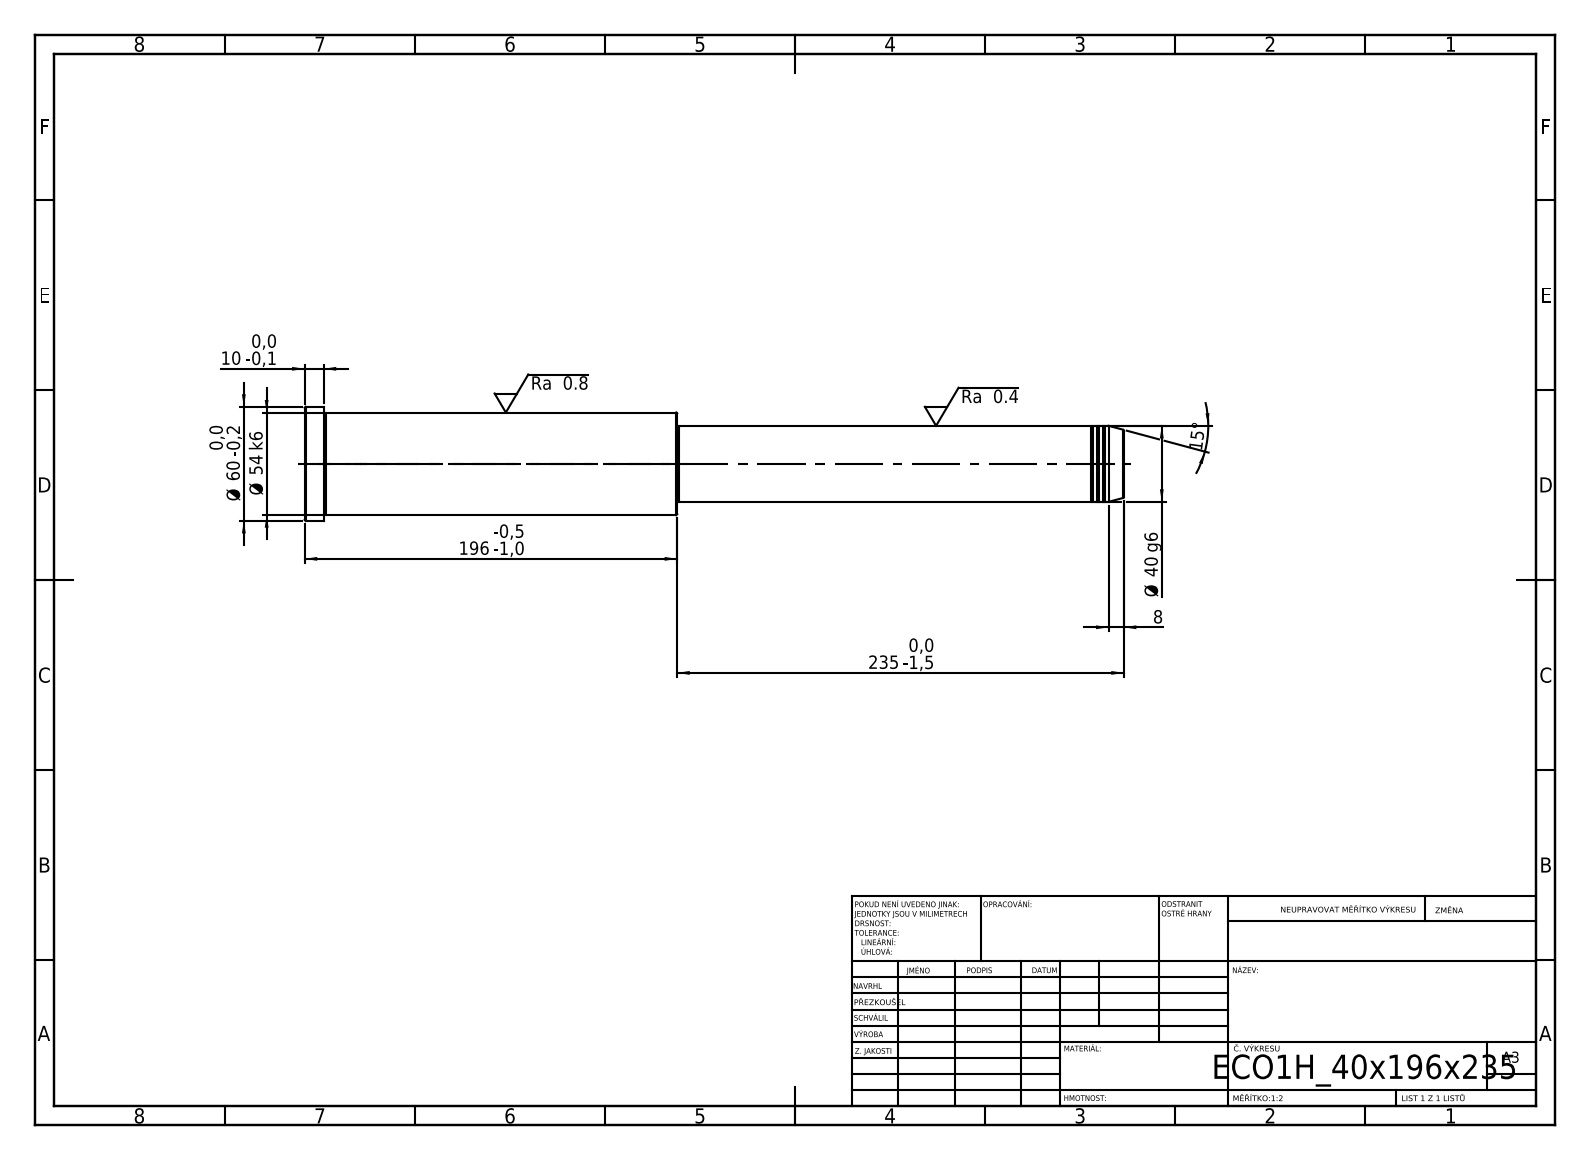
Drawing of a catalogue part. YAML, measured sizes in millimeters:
step_written_by: "SolidWorks 2019 (CONFIG_CONTROL_DESIGN)"
units: millimeters
bodies: {solids: 1, faces: 43, planar: 5, cylindrical: 14, other: 24}
overall_size: [431, 60, 60]
volume: 748204
surface_area: 68652
round_bosses_or_shafts:
  - {diameter: 60, count: 1}
  - {diameter: 54, count: 1}
  - {diameter: 40, count: 1}
  - {diameter: 39, count: 1}
face_to_face_distances: [196, 235, 431, 421, 186, 10, 234, 1, 187, 197]
